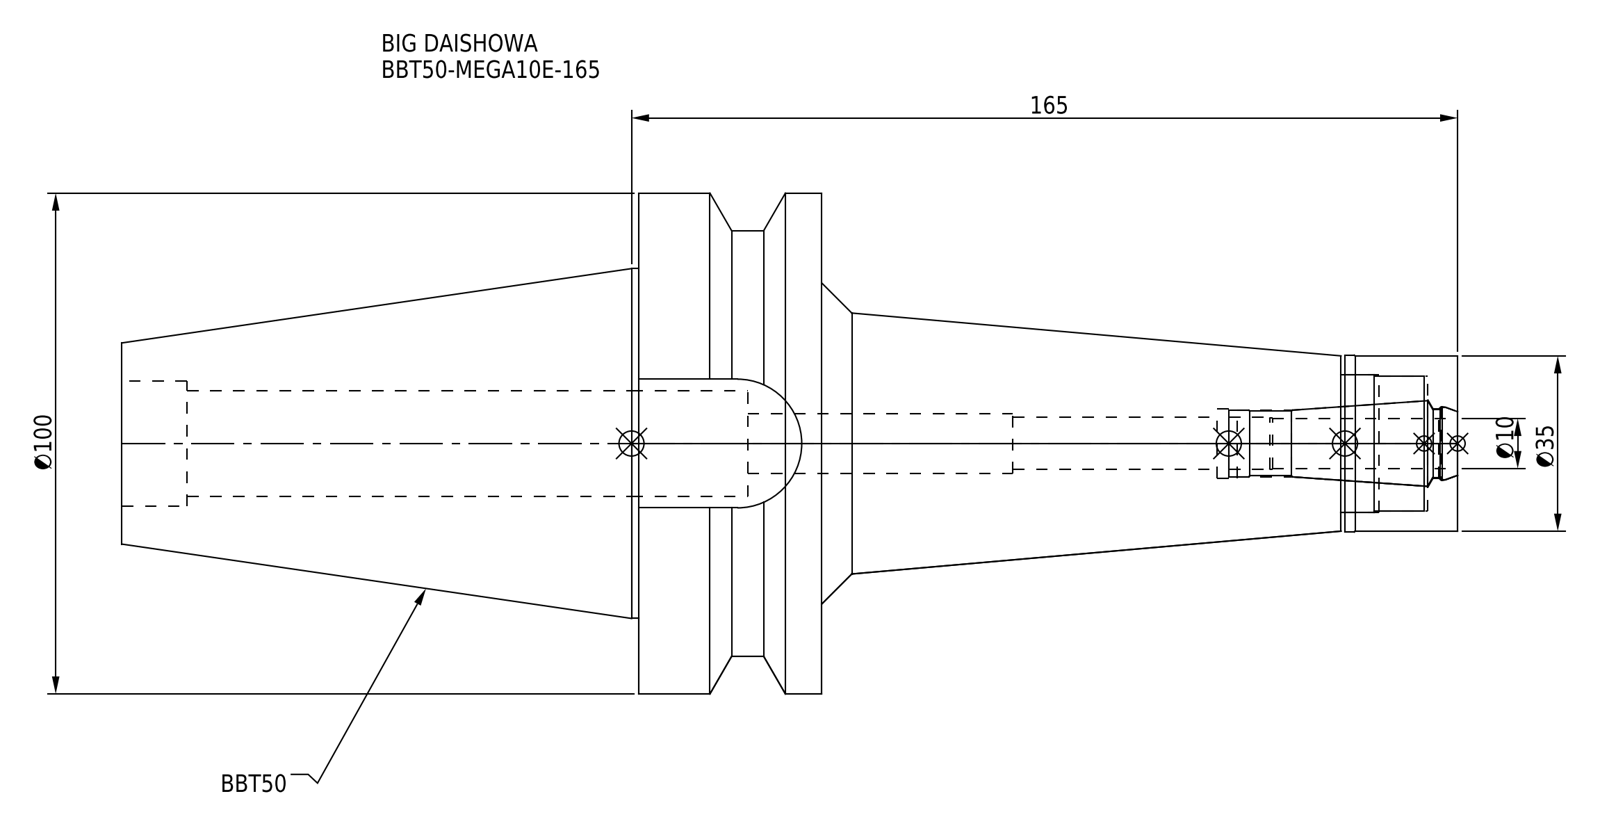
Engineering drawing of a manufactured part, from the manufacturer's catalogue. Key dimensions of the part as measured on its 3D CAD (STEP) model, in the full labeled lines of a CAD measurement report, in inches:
Part name (STEP PRODUCT): BBT50-MEGA10E-165_1.stp; MEN10_1.stp; BBT50-MEGA10E-165-100-FreeParts; BBT50-MEGA10E-165 (+3 more)
STEP written by: SolidWorks 2019 (CONFIG_CONTROL_DESIGN)
Units: inches
Bodies: 2 solids, 81 faces (21 planar, 40 cylindrical, 20 other)
Overall size (bounding box): 10.504 × 3.937 × 3.937
Volume: 37.88 in³ · Surface area: 122.1 in²
Round holes (diameter × count): ⌀0.409 ×1, ⌀0.472 ×1, ⌀0.524 ×1, ⌀0.543 ×1, ⌀0.547 ×1, ⌀0.579 ×1, ⌀0.835 ×1, ⌀0.984 ×1, ⌀1.063 ×1, ⌀1.083 ×1
Round bosses / shafts (diameter × count): ⌀3.937 ×1, ⌀3.346 ×1, ⌀2.75 ×1, ⌀1.39 ×1, ⌀1.378 ×1
Partial cylindrical surfaces — rounded edges, fillets, slot ends (radius × count): R0.506 ×1
Main face-to-face distances: 1.437, 5, 6.437, 10.504, 5.504, 4.067, 2.787, 1.012, 0.886, 4.114
